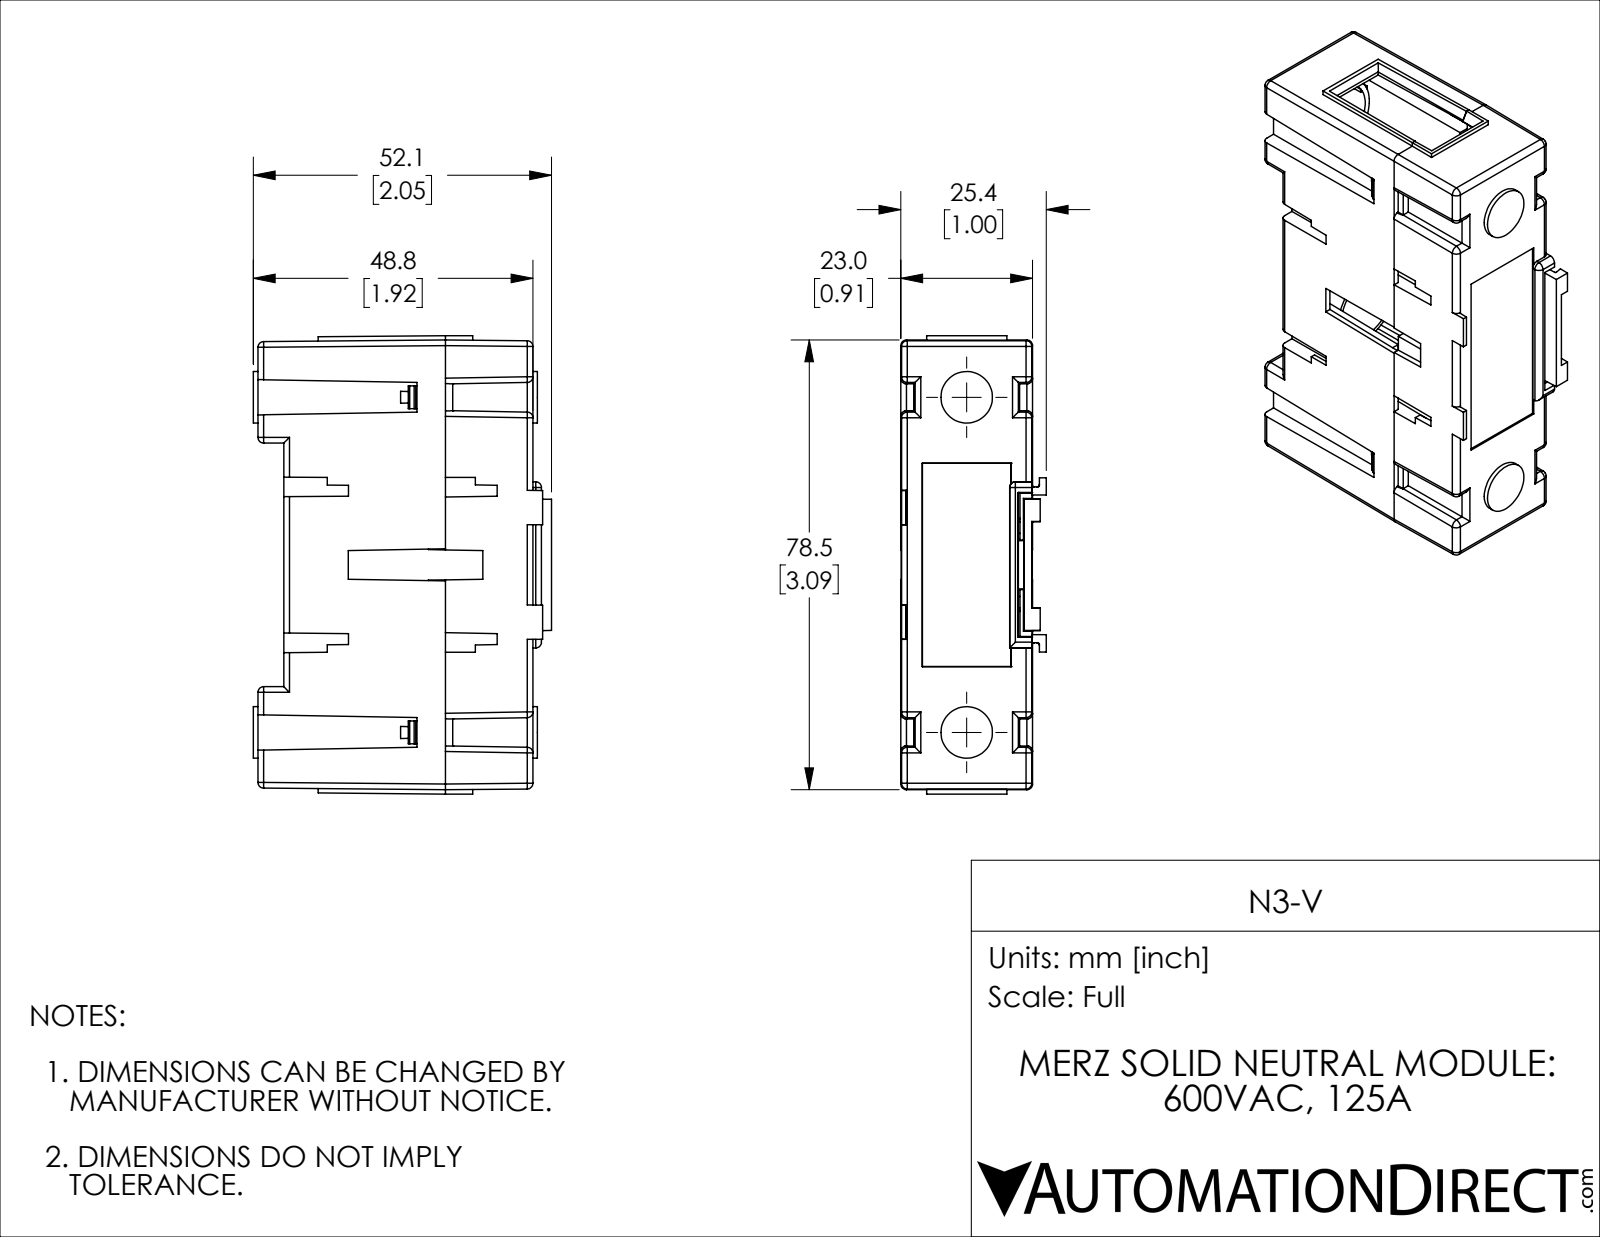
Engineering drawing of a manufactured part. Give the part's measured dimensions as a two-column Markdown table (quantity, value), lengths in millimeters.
| quantity | value |
| --- | --- |
| part name | N3-V |
| STEP written by | SolidWorks 2019 (AUTOMOTIVE_DESIGN) |
| units | millimeters |
| bodies | 1 solid, 849 faces (655 planar, 91 cylindrical, 103 other) |
| overall size | 80 × 52 × 25.4 |
| volume | 22 500 mm³ |
| surface area | 36 340 mm² |
| round bosses / shafts (diameter × count) | 9 × 2 |
| partial cylindrical surfaces (radius × count) | 1 × 42, 0.5 × 6, 0.3 × 4, 2 × 4, 0.2 × 1 |
| main face-to-face distances | 1, 23, 22, 3, 60.5, 0.7, 42.2, 18, 42.5, 18.6 |
